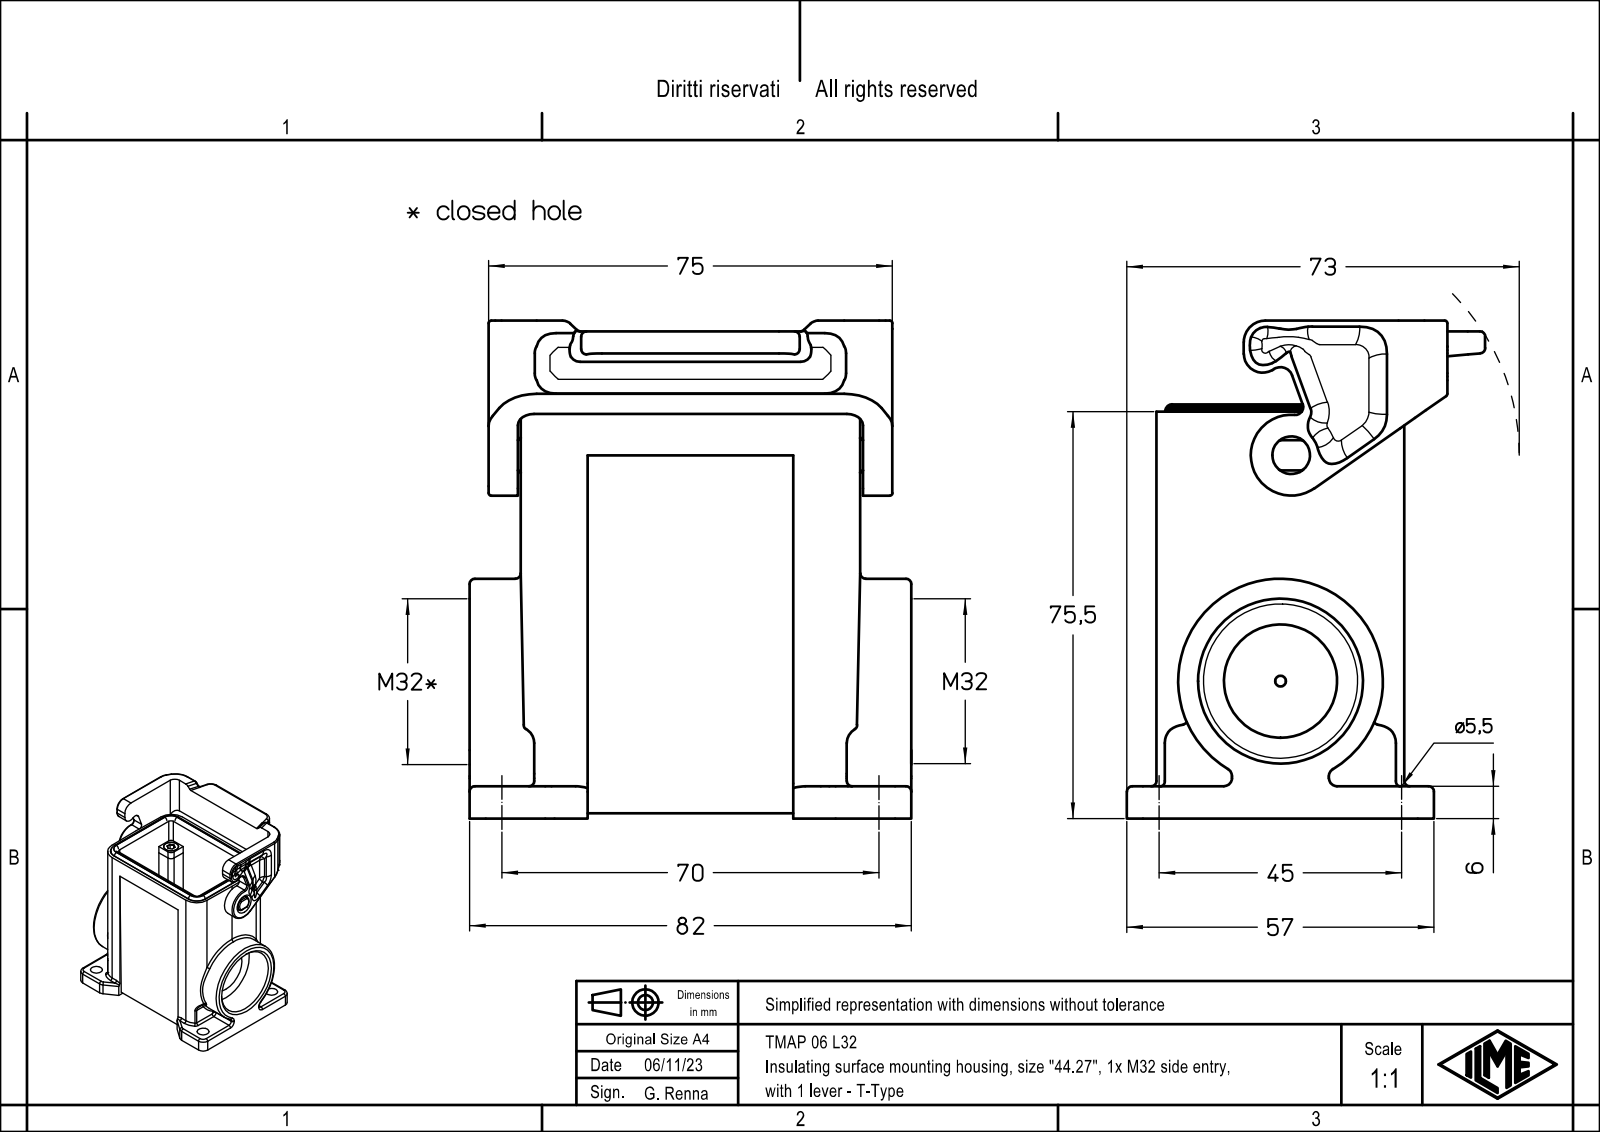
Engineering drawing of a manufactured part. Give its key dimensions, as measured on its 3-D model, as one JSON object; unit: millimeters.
{"part_name": "TMAP 06 L32", "step_written_by": "Creo Elements/Direct Modeling 20.1B 02-Apr-2019 (C) Parametric Technology GmbH (AUTOMOTIVE_DESIGN)", "units": "millimeters", "bodies": {"solids": 1, "faces": 326, "planar": 162, "cylindrical": 128, "other": 36}, "overall_size": [92.4, 82, 66.5], "volume_mm3": 125546, "surface_area_mm2": 47943, "round_holes": [[5.5, 4], [28, 1], [30.6, 1]], "round_bosses_or_shafts": [[38, 1]], "partial_cylinders_radius": [[3, 17], [2, 10], [1.5, 9], [1, 8], [1.3, 8], [0.5, 4], [6, 4], [7, 4]], "face_to_face_distances": [5.4, 40.6, 46, 35.2, 5.5, 1, 14.9, 9, 58.1, 5.9], "hole_center_spacings": [45, 70, 83.22]}
